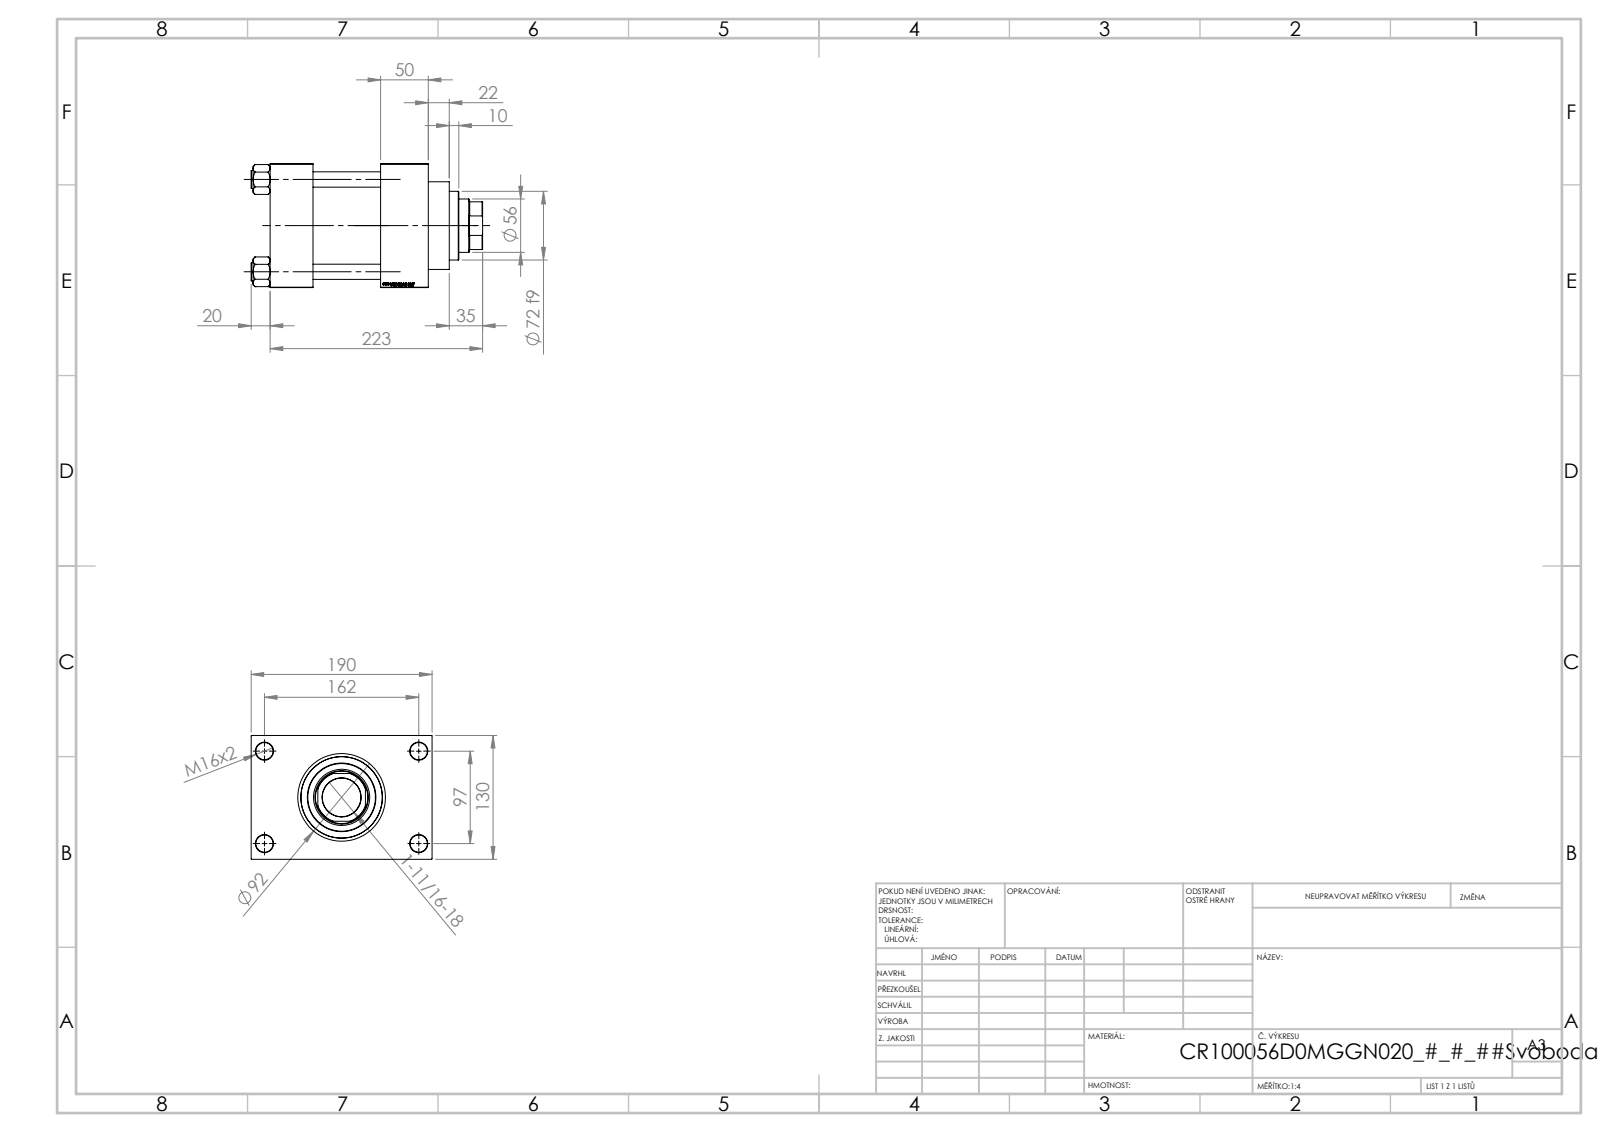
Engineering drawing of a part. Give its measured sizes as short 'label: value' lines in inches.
name: NUT_M5_D; V215CR_D_TYCINKA; V215_VC_A; V215CR_VCP_D (+1 more)
written by: SolidWorks 2019 (CONFIG_CONTROL_DESIGN)
unit: in
bodies: 11 solids, 1152 faces (545 planar, 89 cylindrical, 518 other)
size: 9.567 × 7.48 × 5.118
volume: 161.3 in³; area: 557.8 in²
holes: 4× ⌀0.63, 4× ⌀0.709, 2× ⌀0.276, 2× ⌀1.041, 2× ⌀1.378, 1× ⌀1.594, 1× ⌀2.205, 1× ⌀2.323, 1× ⌀2.992, 1× ⌀3.366, 1× ⌀3.937
bosses: 4× ⌀0.748, 1× ⌀4.173, 1× ⌀3.622, 1× ⌀2.835
rounds: 1× R1.063
face distances: 5.118, 4.567, 1.969, 1.772, 2.795, 6.535, 4.764, 1.181, 6.299, 7.48
hole spacings: 1.281, 2.698, 3.717, 3.815, 4.026, 5.096, 6.367, 3.819
